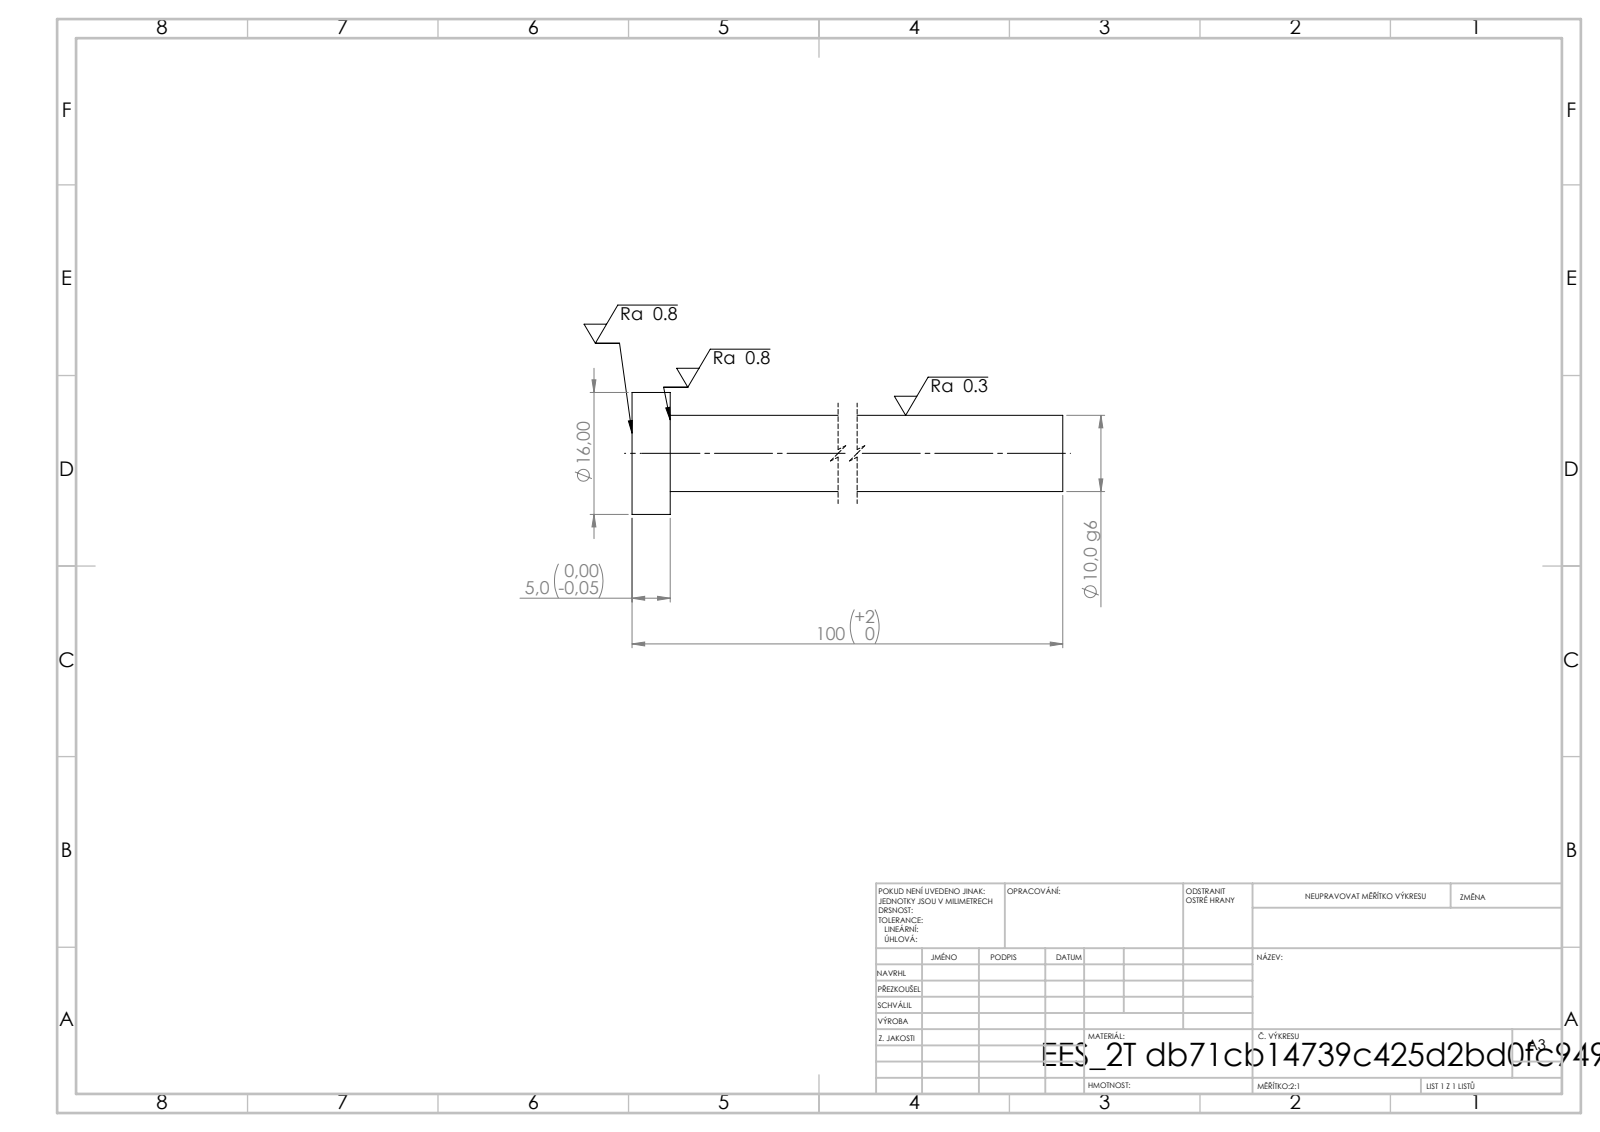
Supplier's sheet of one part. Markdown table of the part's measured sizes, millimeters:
| quantity | value |
| --- | --- |
| STEP written by | SolidWorks 2019 (CONFIG_CONTROL_DESIGN) |
| units | millimeters |
| bodies | 1 solid, 7 faces (3 planar, 4 cylindrical, 0 other) |
| overall size | 100 × 16 × 16 |
| volume | 8 467 mm³ |
| surface area | 3 638 mm² |
| round bosses / shafts (diameter × count) | 16 × 1, 10 × 1 |
| main face-to-face distances | 5, 100, 95 |
